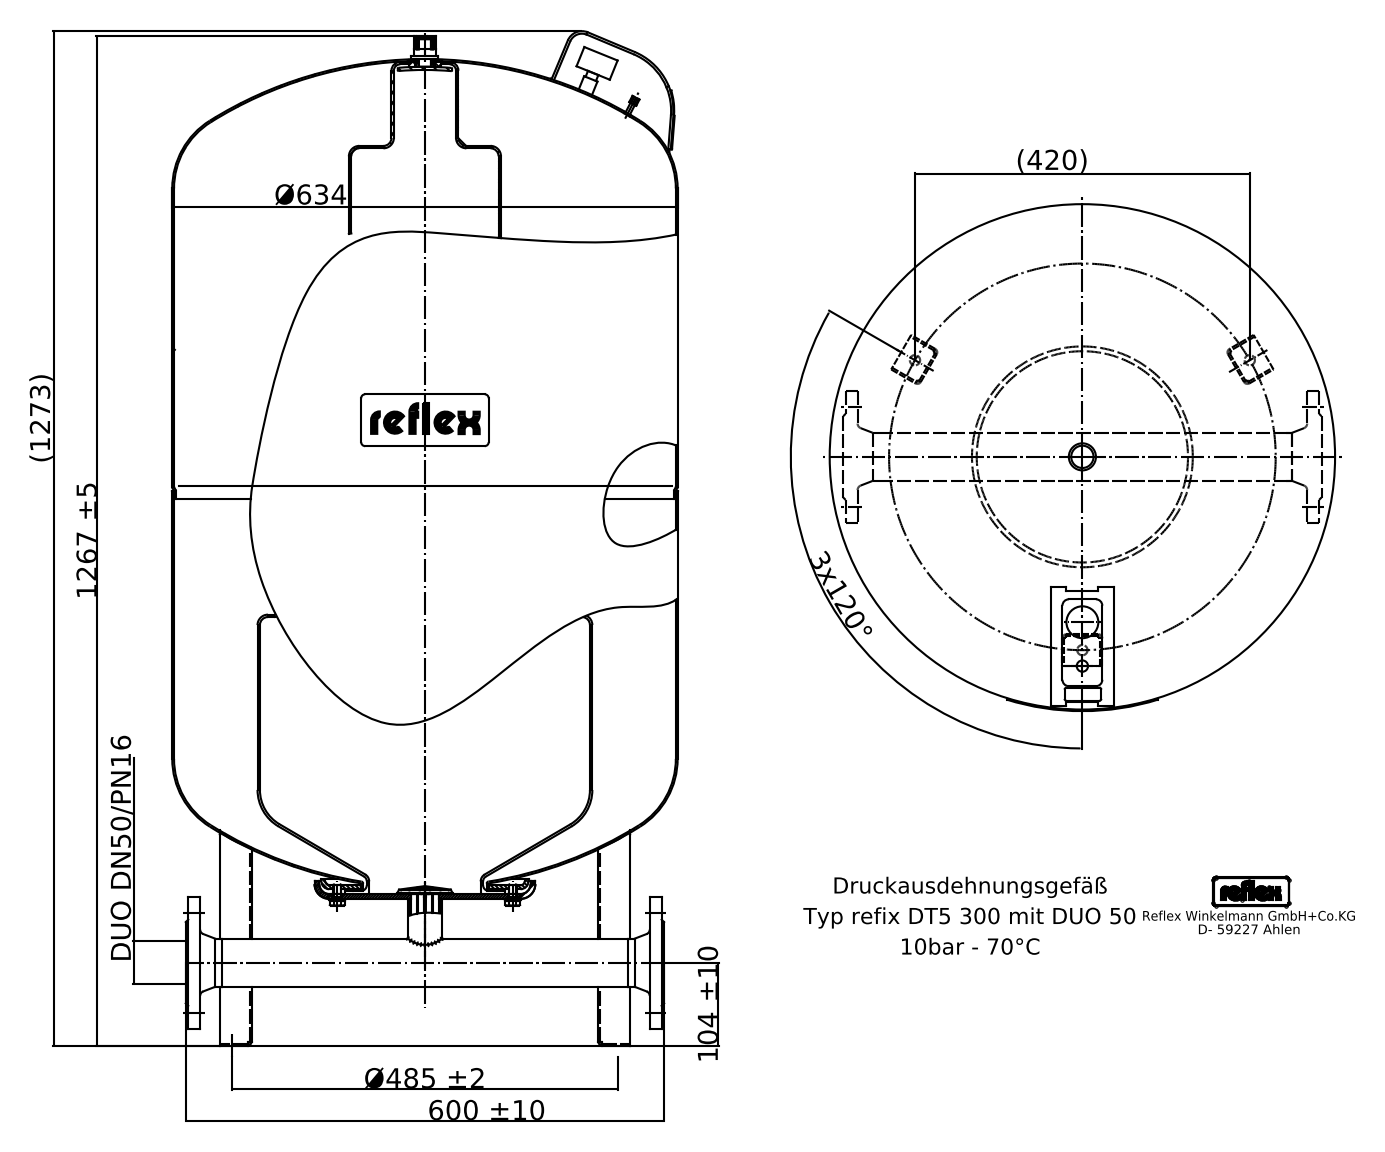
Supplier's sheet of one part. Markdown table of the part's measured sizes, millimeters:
| quantity | value |
| --- | --- |
| STEP written by | Mechanical Desktop 2008 (CONFIG_CONTROL_DESIGN) |
| units | millimeters |
| bodies | 23 solids, 521 faces (223 planar, 185 cylindrical, 113 other) |
| overall size | 1268.4 × 634 × 634 |
| volume | 296 500 000 mm³ |
| surface area | 4 289 000 mm² |
| round holes (diameter × count) | 19 × 4, 13.4 × 3, 2.48 × 1, 3.8 × 1, 4.3 × 1, 4.4 × 1, 5.45 × 1, 7 × 1, 8 × 1, 11.4 × 1, 60.3 × 1, 157 × 1 |
| round bosses / shafts (diameter × count) | 10 × 9, 634 × 1, 260 × 1, 230 × 1, 165 × 1, 62 × 1, 42.4 × 1, 34 × 1 |
| partial cylindrical surfaces (radius × count) | 1 × 15, 2.5 × 15, 5 × 15, 5.62 × 4, 2.25 × 3, 3.84 × 2, 6.75 × 2, 8 × 2 |
| main face-to-face distances | 716, 2.5, 47.5, 170, 886, 6, 176, 892, 50, 45 |
| hole center spacings | 62.49, 88.38, 242.5, 420.02, 124.99 |
